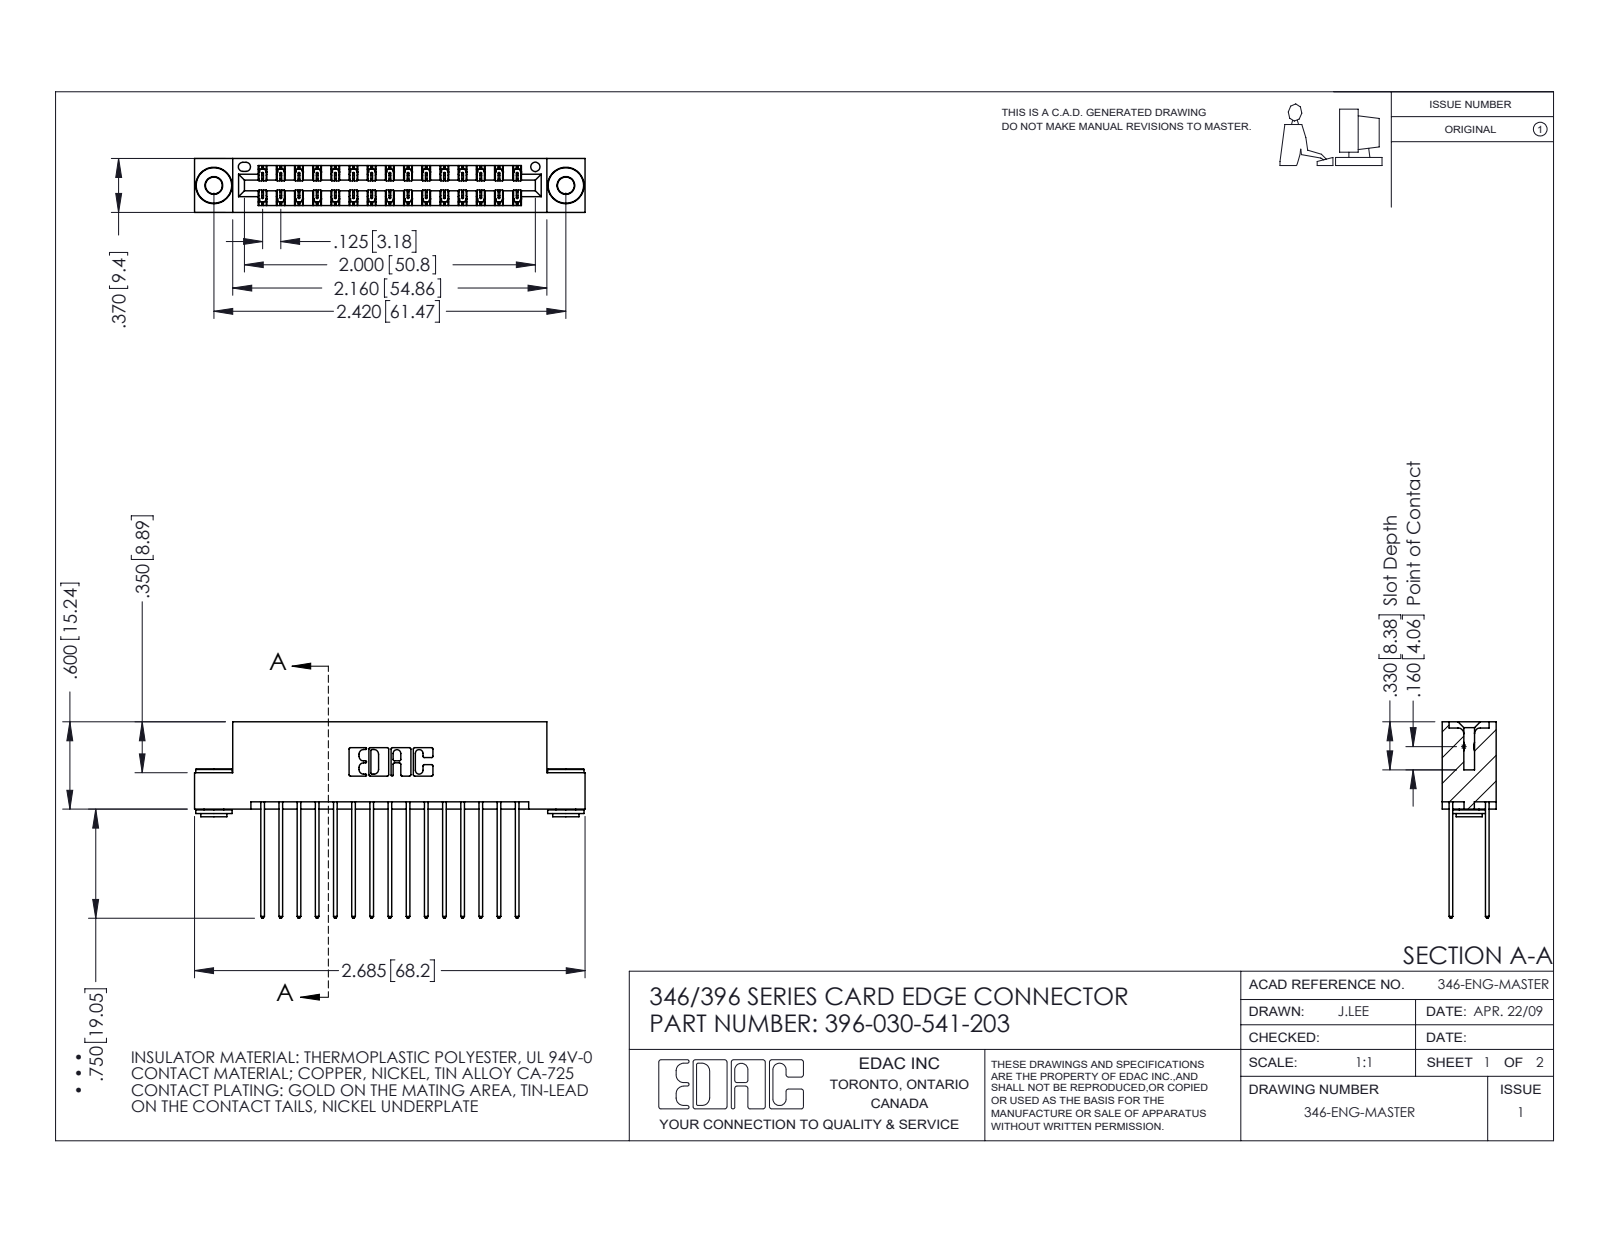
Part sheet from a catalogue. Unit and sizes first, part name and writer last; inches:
Units: inches
Overall size (bounding box): 2.685 × 1.35 × 0.37
Round holes (diameter × count): ⌀0.116 ×2, ⌀0.156 ×2, ⌀0.064 ×1
Round bosses / shafts (diameter × count): ⌀0.25 ×2, ⌀0.18 ×2, ⌀0.136 ×2
Partial cylindrical surfaces — rounded edges, fillets, slot ends (radius × count): R0.006 ×45, R0.01 ×30, R0.01 ×22, R0.007 ×6, R0.031 ×6, R0.026 ×3, R0.014 ×2, R0.022 ×2
Main face-to-face distances: 0.25, 0.048, 0.322, 0.025, 0.072, 0.298, 0.37, 0.275, 0.225, 0.148
Hole centre spacings: 0.246, 2.213, 2.42
Volume: 0.405 in³ · Surface area: 15.08 in²
Bodies: 33 solids, 1720 faces (1136 planar, 576 cylindrical, 8 other)
Part name (STEP PRODUCT): 345-292-001_345-293-141; 396-030-541-203; 345-250-002_345-250-002-102; 346 Part_Flush Mounting Lugs - 0.156 Dia-TH
STEP written by: SolidWorks 2016 (CONFIG_CONTROL_DESIGN)
